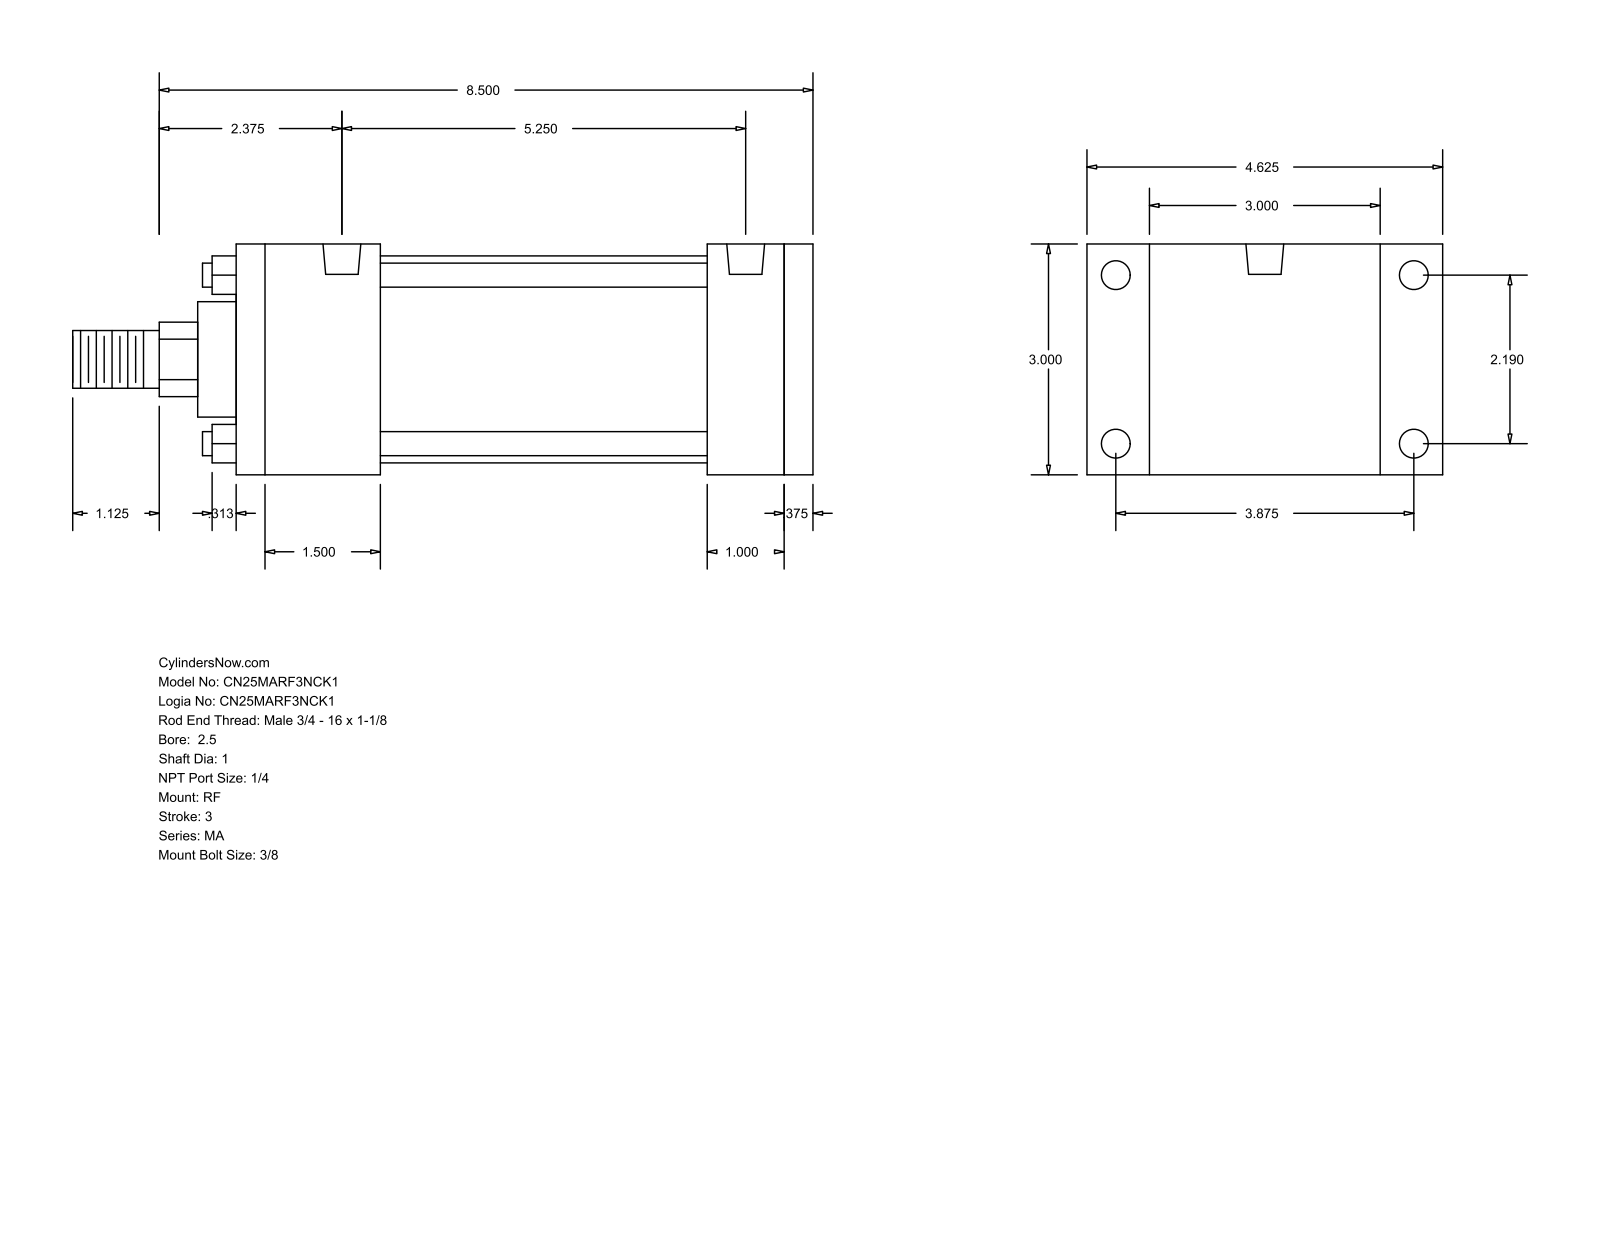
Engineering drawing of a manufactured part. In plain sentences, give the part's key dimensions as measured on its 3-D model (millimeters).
The part is named "MA_RF__0250_1". Its 3-D file was written by "GSSL Pune (CONFIG_CONTROL_DESIGN)". It is 0 solids with 92 faces: 64 planar, 28 cylindrical and 0 other. Overall it measures 244.47 by 117.47 by 76.2 millimeters. Round holes: 4 of diameter 7.94, 4 of diameter 9.53, 2 of diameter 12.49. Round bosses or shafts: 4 of diameter 7.94, 1 of diameter 68.33, 1 of diameter 38.1, 1 of diameter 25.4, 1 of diameter 19.05. Partial cylindrical surfaces (rounded edges, fillets, slot ends): 1 of radius 12.29. The main face-to-face distances are 76.2, 190.5, 180.98, 9.52, 47.63, 155.57, 107.94, 133.35, 142.87, 25.41. The hole center spacings are 55.62, 98.42, 113.05, 133.35.
